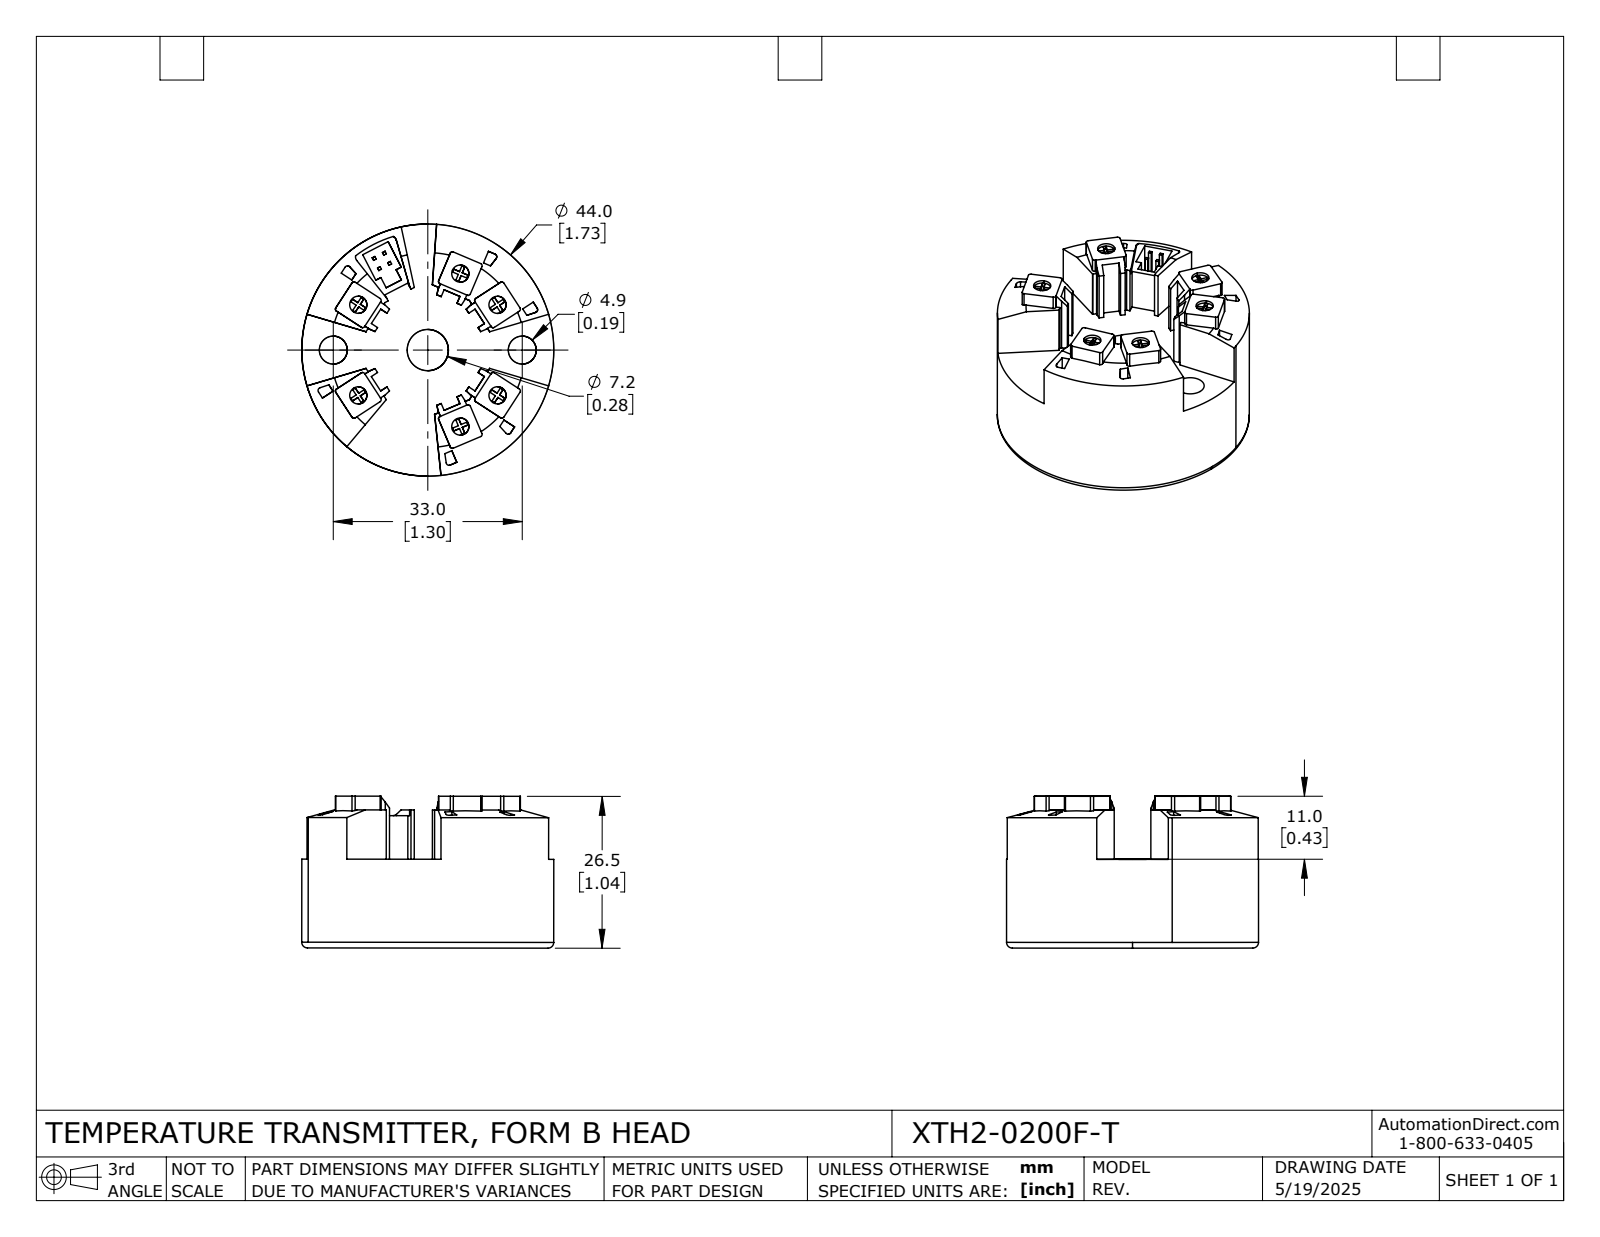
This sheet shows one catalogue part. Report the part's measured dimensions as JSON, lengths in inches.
{"part_name": "XTDH2-0200F-T", "step_written_by": "SolidWorks 2024 (AUTOMOTIVE_DESIGN)", "units": "inches", "bodies": {"solids": 1, "faces": 341, "planar": 281, "cylindrical": 52, "other": 8}, "overall_size": [1.733, 1.732, 1.045], "volume_in3": 1.748, "surface_area_in2": 13.46, "round_holes": [[0.118, 6], [0.193, 2], [0.283, 1]], "round_bosses_or_shafts": [[1.732, 1]], "partial_cylinders_radius": [[0.016, 24], [0.02, 6], [0.039, 2]], "face_to_face_distances": [0.61, 1.043, 0.433, 0.059, 0.177, 0.039, 0.02, 0.118, 0.949, 0.339], "hole_center_spacings": [0.571, 0.333, 0.355, 0.356, 0.65, 0.677, 0.733, 0.875]}
